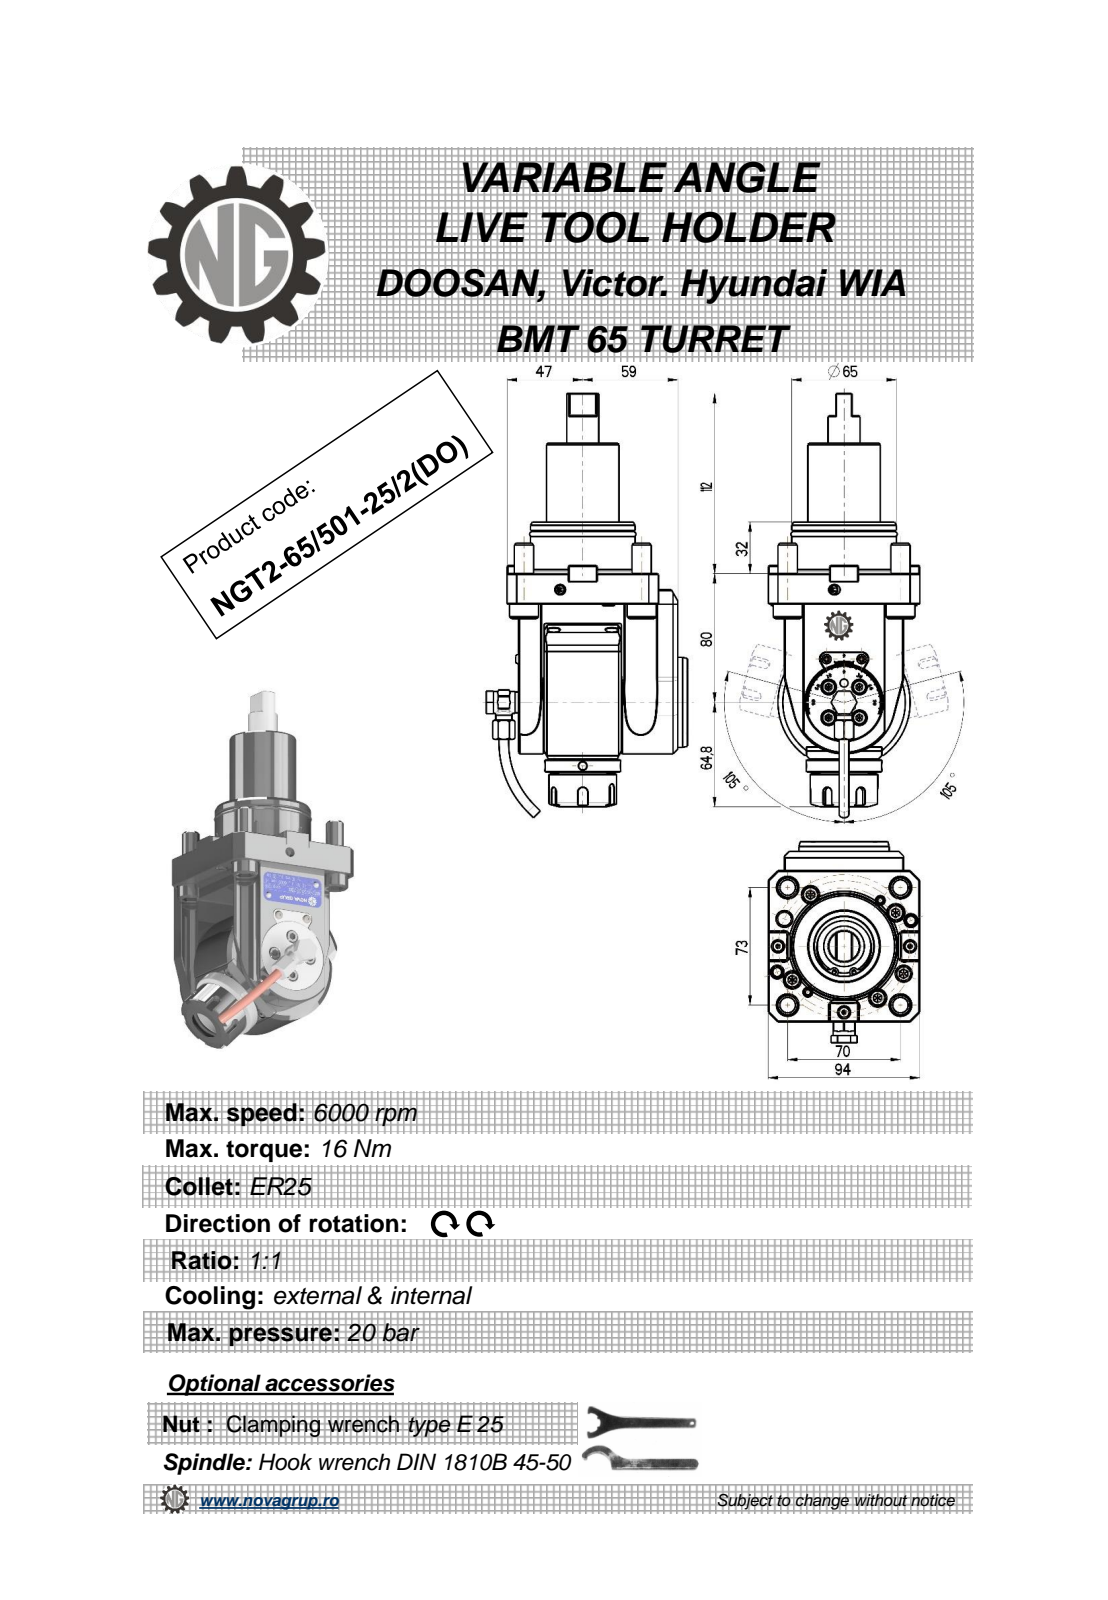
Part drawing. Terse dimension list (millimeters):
name: NGT2_65_501_25_2_DO
written by: PRO/ENGINEER BY PARAMETRIC TECHNOLOGY CORPORATION, 2010280 (CONFIG_CONTROL_DESIGN)
unit: mm
bodies: 2 solids, 649 faces (281 planar, 184 cylindrical, 184 other)
size: 263.67 × 124.9 × 94
volume: 1 009 000 mm³; area: 103 538 mm²
holes: 3× ⌀4, 2× ⌀5, 2× ⌀8.5, 1× ⌀3, 1× ⌀6.2, 1× ⌀9, 1× ⌀11, 1× ⌀20.3, 1× ⌀34
bosses: 4× ⌀18, 4× ⌀12, 2× ⌀10, 2× ⌀8, 2× ⌀6, 2× ⌀5.7, 1× ⌀65, 1× ⌀64.4
rounds: 20× R0.36, 12× R0.41, 6× R0.51, 6× R10, 5× R3, 4× R0.5, 2× R0.8, 2× R1
face distances: 31, 12, 10, 99, 23, 112, 84, 6, 94, 71
hole spacings: 40.72, 0.4, 39.45, 48.92, 49, 49.18, 49.4, 75.66
